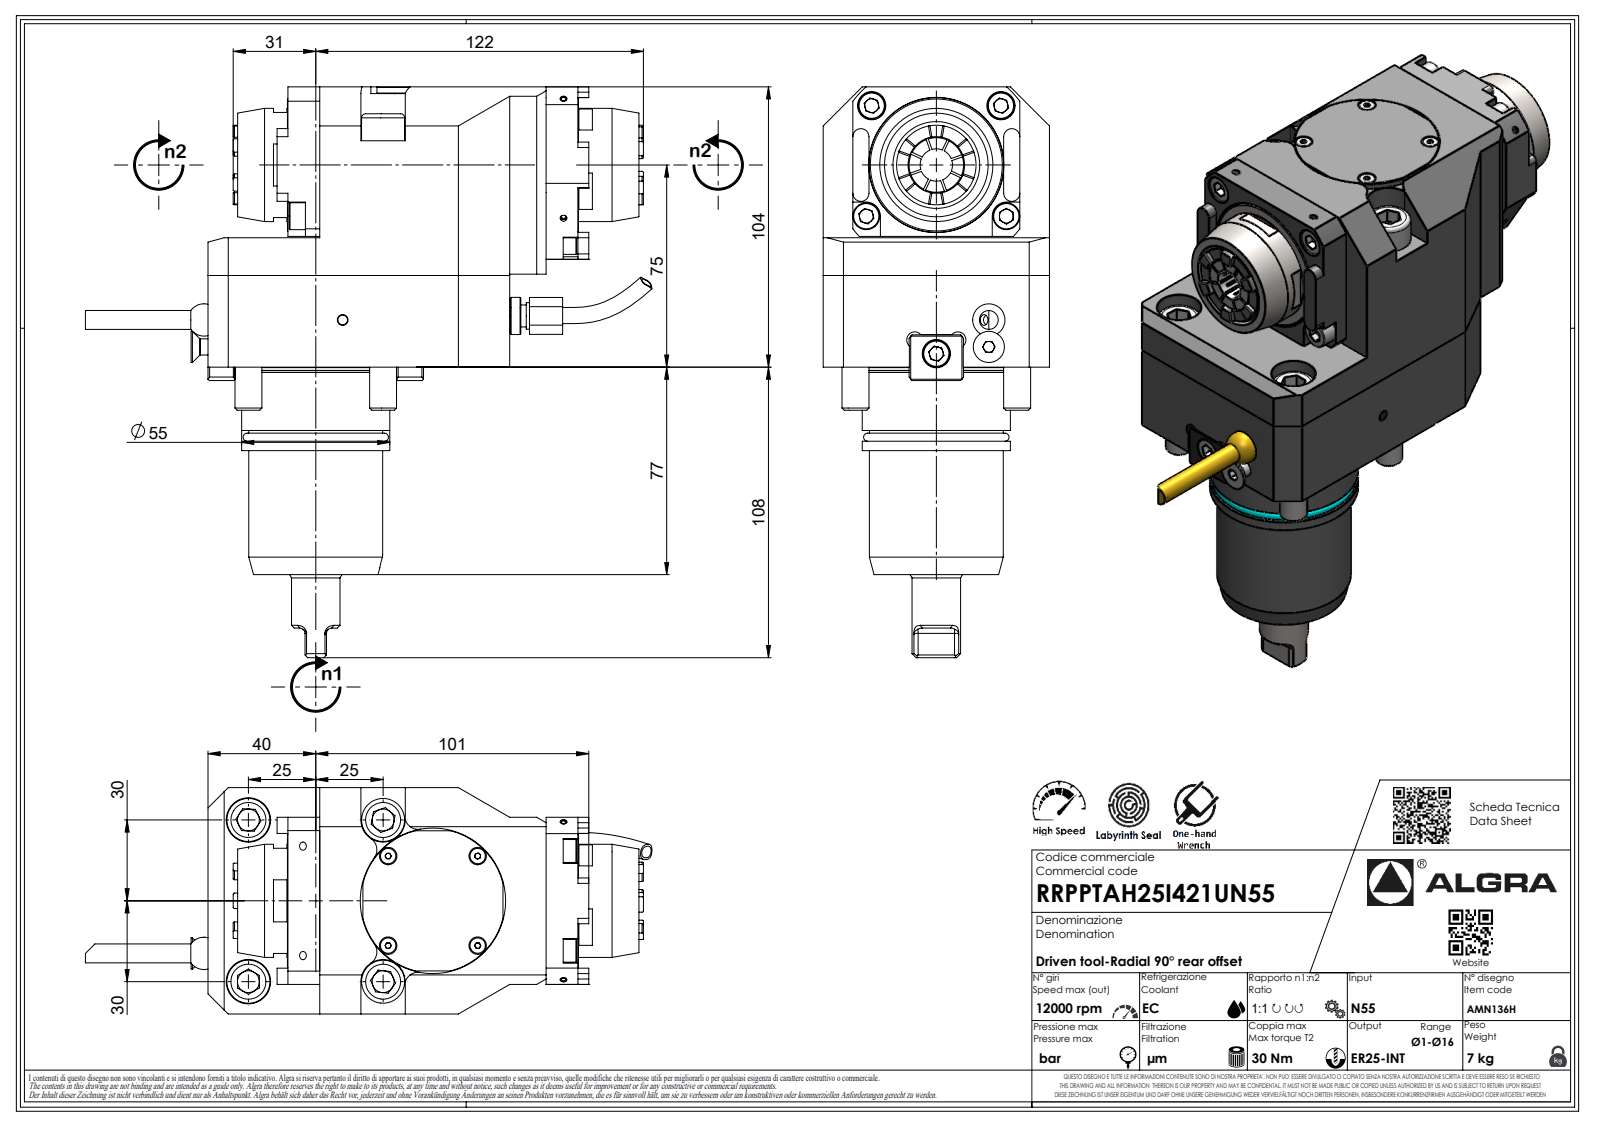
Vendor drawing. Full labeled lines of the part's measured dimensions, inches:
Part name (STEP PRODUCT): RRPPTAH25I421UN55
STEP written by: SolidWorks 2023 (AUTOMOTIVE_DESIGN)
Units: inches
Bodies: 1 solid, 630 faces (431 planar, 96 cylindrical, 103 other)
Overall size (bounding box): 8.339 × 8.28 × 3.307
Volume: 68.1 in³ · Surface area: 136.2 in²
Round holes (diameter × count): ⌀0.083 ×1, ⌀0.157 ×1
Round bosses / shafts (diameter × count): ⌀0.394 ×4, ⌀0.63 ×2, ⌀2.165 ×1, ⌀2.15 ×1, ⌀1.957 ×1, ⌀1.654 ×1, ⌀0.709 ×1, ⌀0.386 ×1
Partial cylindrical surfaces — rounded edges, fillets, slot ends (radius × count): R0.079 ×19, R0.013 ×7, R0.02 ×7, R0.146 ×7, R0.118 ×4, R0.325 ×3, R0.157 ×2, R0.197 ×2
Main face-to-face distances: 3.307, 0.433, 1.89, 2.874, 2.205, 4.094, 1.882, 4.087, 2.441, 4.409
